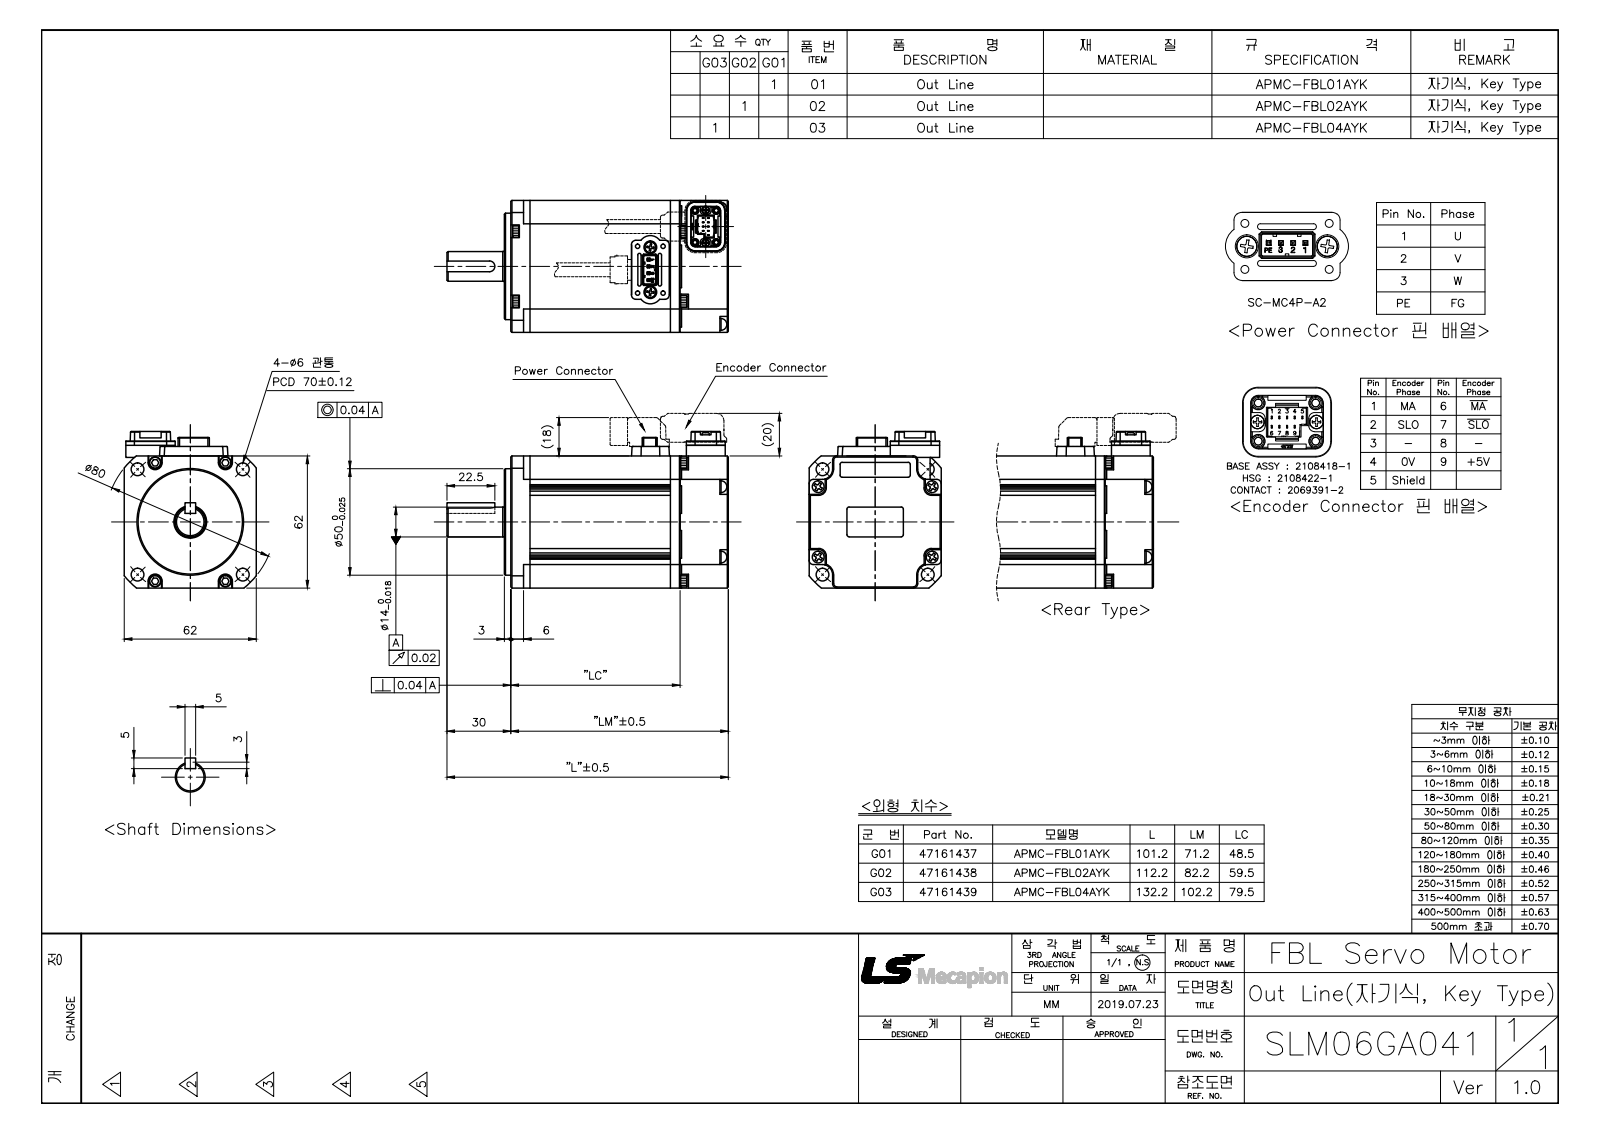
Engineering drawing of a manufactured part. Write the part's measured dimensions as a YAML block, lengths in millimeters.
part_name: "SLM06GA041G01_Out Line(APMC-FBL01AYK)"
step_written_by: "SolidWorks 2011 (AUTOMOTIVE_DESIGN)"
units: millimeters
bodies: {solids: 45, faces: 1850, planar: 1191, cylindrical: 470, other: 189}
overall_size: [101.2, 73.5, 62]
volume: 254627
surface_area: 68113
round_holes:
  - {diameter: 2.1, count: 10}
  - {diameter: 3, count: 10}
  - {diameter: 3.5, count: 8}
  - {diameter: 1.6, count: 6}
  - {diameter: 6, count: 6}
  - {diameter: 3.1, count: 4}
  - {diameter: 3.3, count: 1}
  - {diameter: 3.4, count: 1}
  - {diameter: 15.3, count: 1}
round_bosses_or_shafts:
  - {diameter: 5.4, count: 6}
  - {diameter: 5.6, count: 4}
  - {diameter: 5.5, count: 4}
  - {diameter: 2.2, count: 2}
  - {diameter: 50, count: 1}
  - {diameter: 15, count: 1}
  - {diameter: 14.8, count: 1}
  - {diameter: 14, count: 1}
partial_cylinders:
  - {radius: 0.2, count: 20}
  - {radius: 0.3, count: 20}
  - {radius: 3, count: 12}
  - {radius: 1, count: 10}
  - {radius: 0.15, count: 9}
  - {radius: 2, count: 8}
  - {radius: 0.45, count: 7}
  - {radius: 0.11, count: 6}
face_to_face_distances: [4.5, 35, 0.7, 5.2, 39.5, 40.2, 62, 9, 3, 22]
hole_center_spacings: [5, 6.02, 8.5, 8.8, 15.29, 16, 22.32, 31.47]
